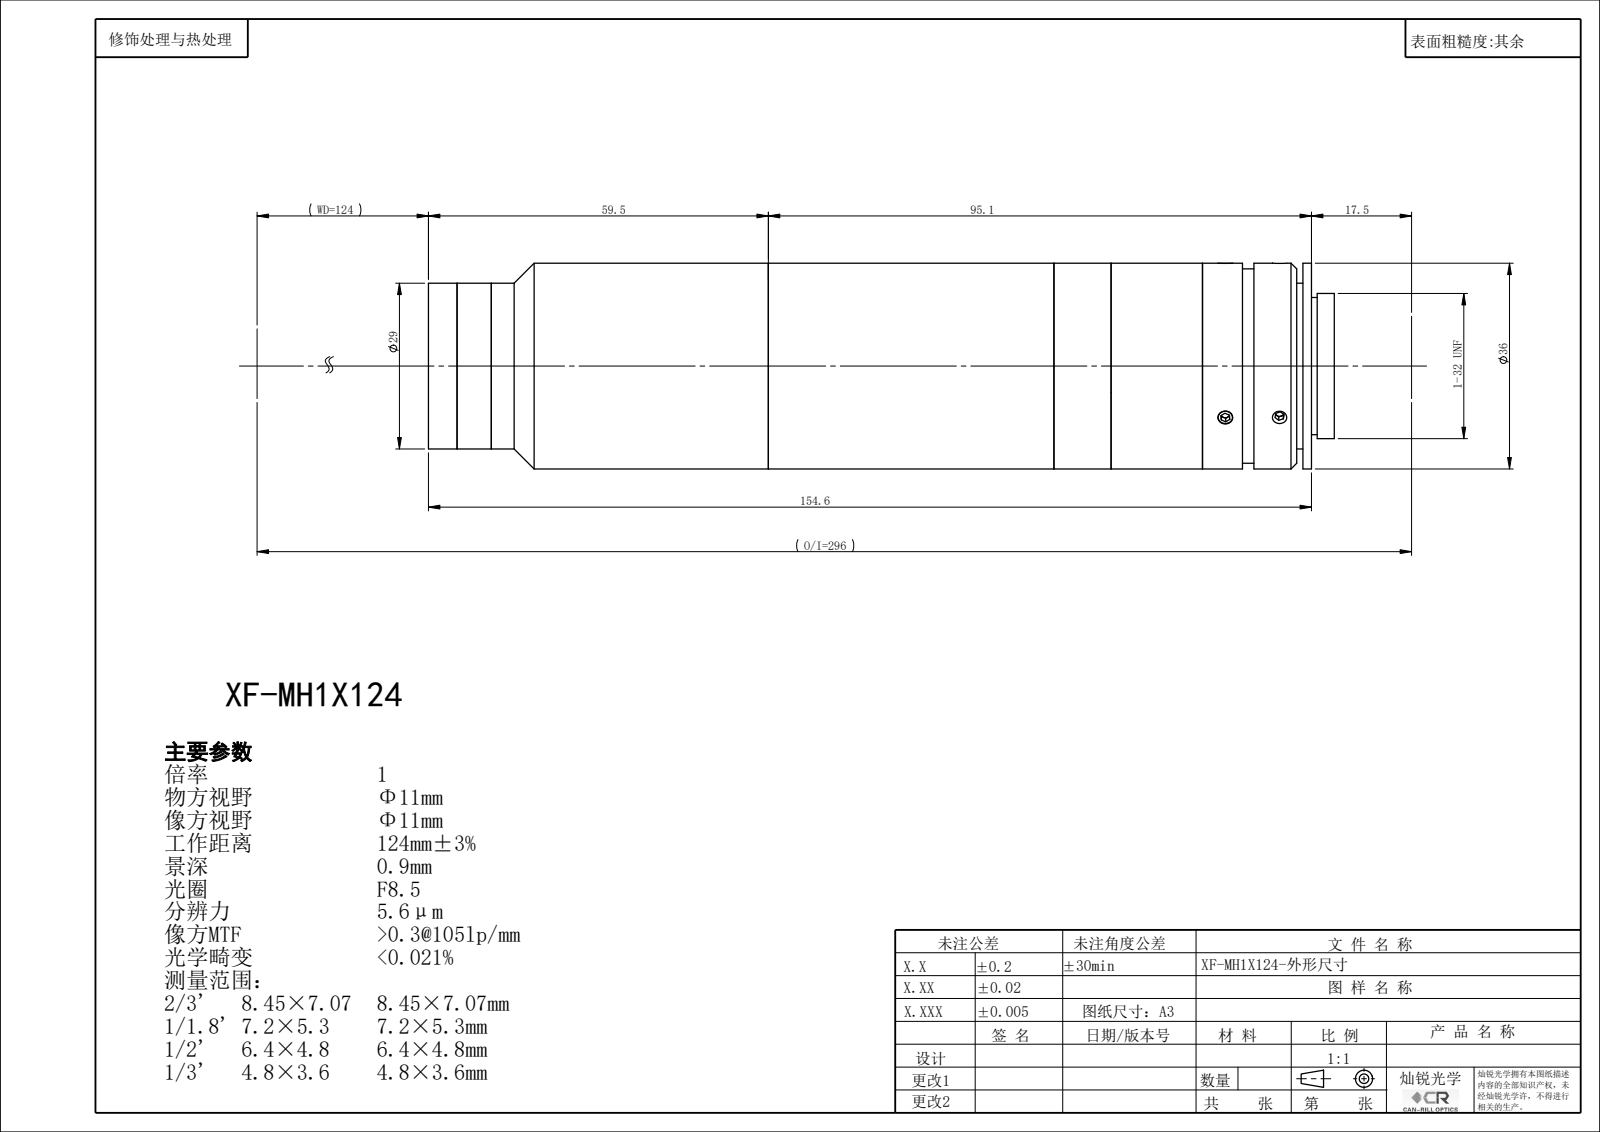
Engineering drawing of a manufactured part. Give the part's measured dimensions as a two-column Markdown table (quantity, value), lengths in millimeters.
| quantity | value |
| --- | --- |
| part name | XF-MH1X124 |
| STEP written by | SolidWorks 2022 (CONFIG_CONTROL_DESIGN) |
| units | millimeters |
| bodies | 0 solids, 129 faces (63 planar, 44 cylindrical, 22 other) |
| overall size | 158.58 × 36 × 36 |
| round holes (diameter × count) | 2.5 × 3, 18 × 1, 22.4 × 1, 24 × 1, 24.9 × 1, 26.4 × 1 |
| round bosses / shafts (diameter × count) | 36 × 1, 34 × 1, 29 × 1, 25.4 × 1 |
| main face-to-face distances | 19.08, 1.5, 17.58, 16, 33.58, 35.08, 10, 26, 43.58, 45.08 |
